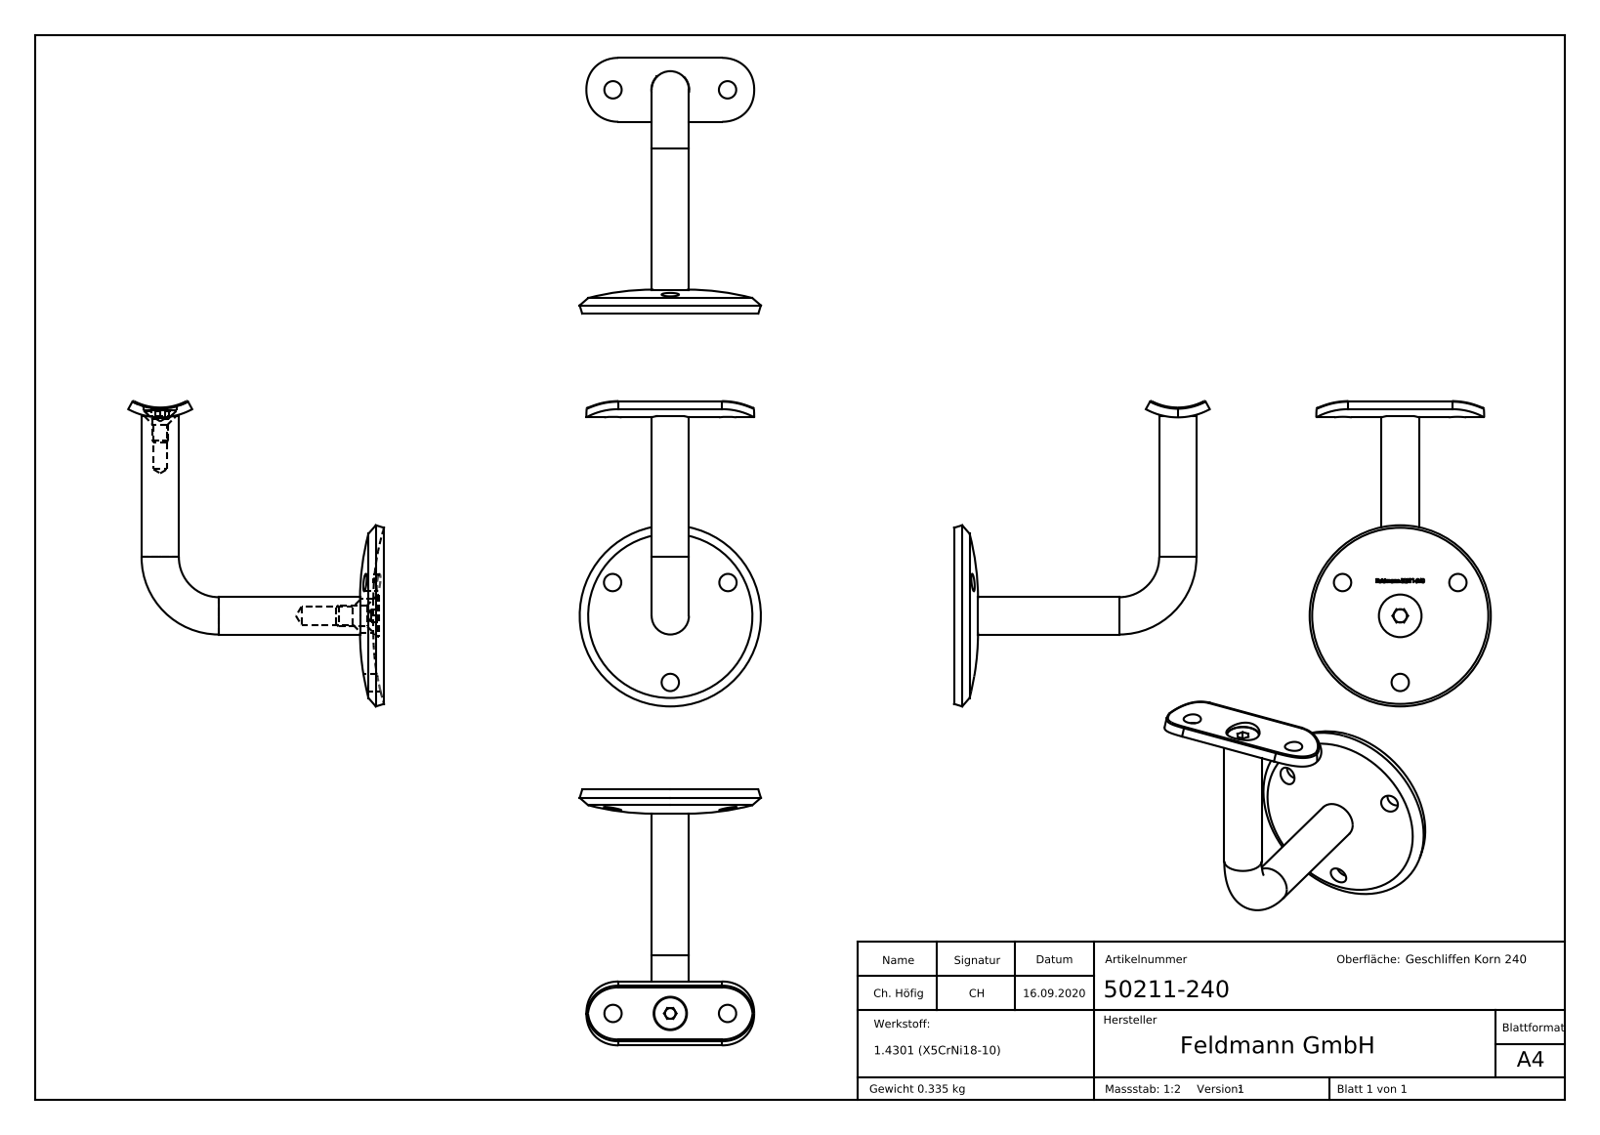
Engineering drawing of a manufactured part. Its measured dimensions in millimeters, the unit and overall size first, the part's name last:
Units: millimetres
Overall size (bounding box): 114.65 × 96 × 68
Round holes (diameter × count): ⌀6.5 ×5, ⌀12.5 ×2, ⌀5 ×1, ⌀6.8 ×1
Round bosses / shafts (diameter × count): ⌀14 ×2, ⌀16 ×1, ⌀12 ×1, ⌀8 ×1, ⌀6 ×1
Partial cylindrical surfaces — rounded edges, fillets, slot ends (radius × count): R12 ×4, R0.5 ×2, R7.1 ×1, R21.2 ×1, R24.9 ×1
Main face-to-face distances: 2.2, 7.15, 16, 8.85, 5, 4, 9.8, 12, 62.7, 72.5
Hole centre spacings: 25, 43.3, 21.5, 43
Volume: 42 397 mm³ · Surface area: 19 877 mm²
Bodies: 5 solids, 320 faces (134 planar, 41 cylindrical, 145 other)
Part name (STEP PRODUCT): DIN-7991 M3-M10; DIN-7991 M3-M10_DIN7991 M8x16; 50211-240 Teil3_50211-240 Teil3; 50211-240 Teil2 (+6 more)
STEP written by: SolidWorks 2018 (CONFIG_CONTROL_DESIGN)
